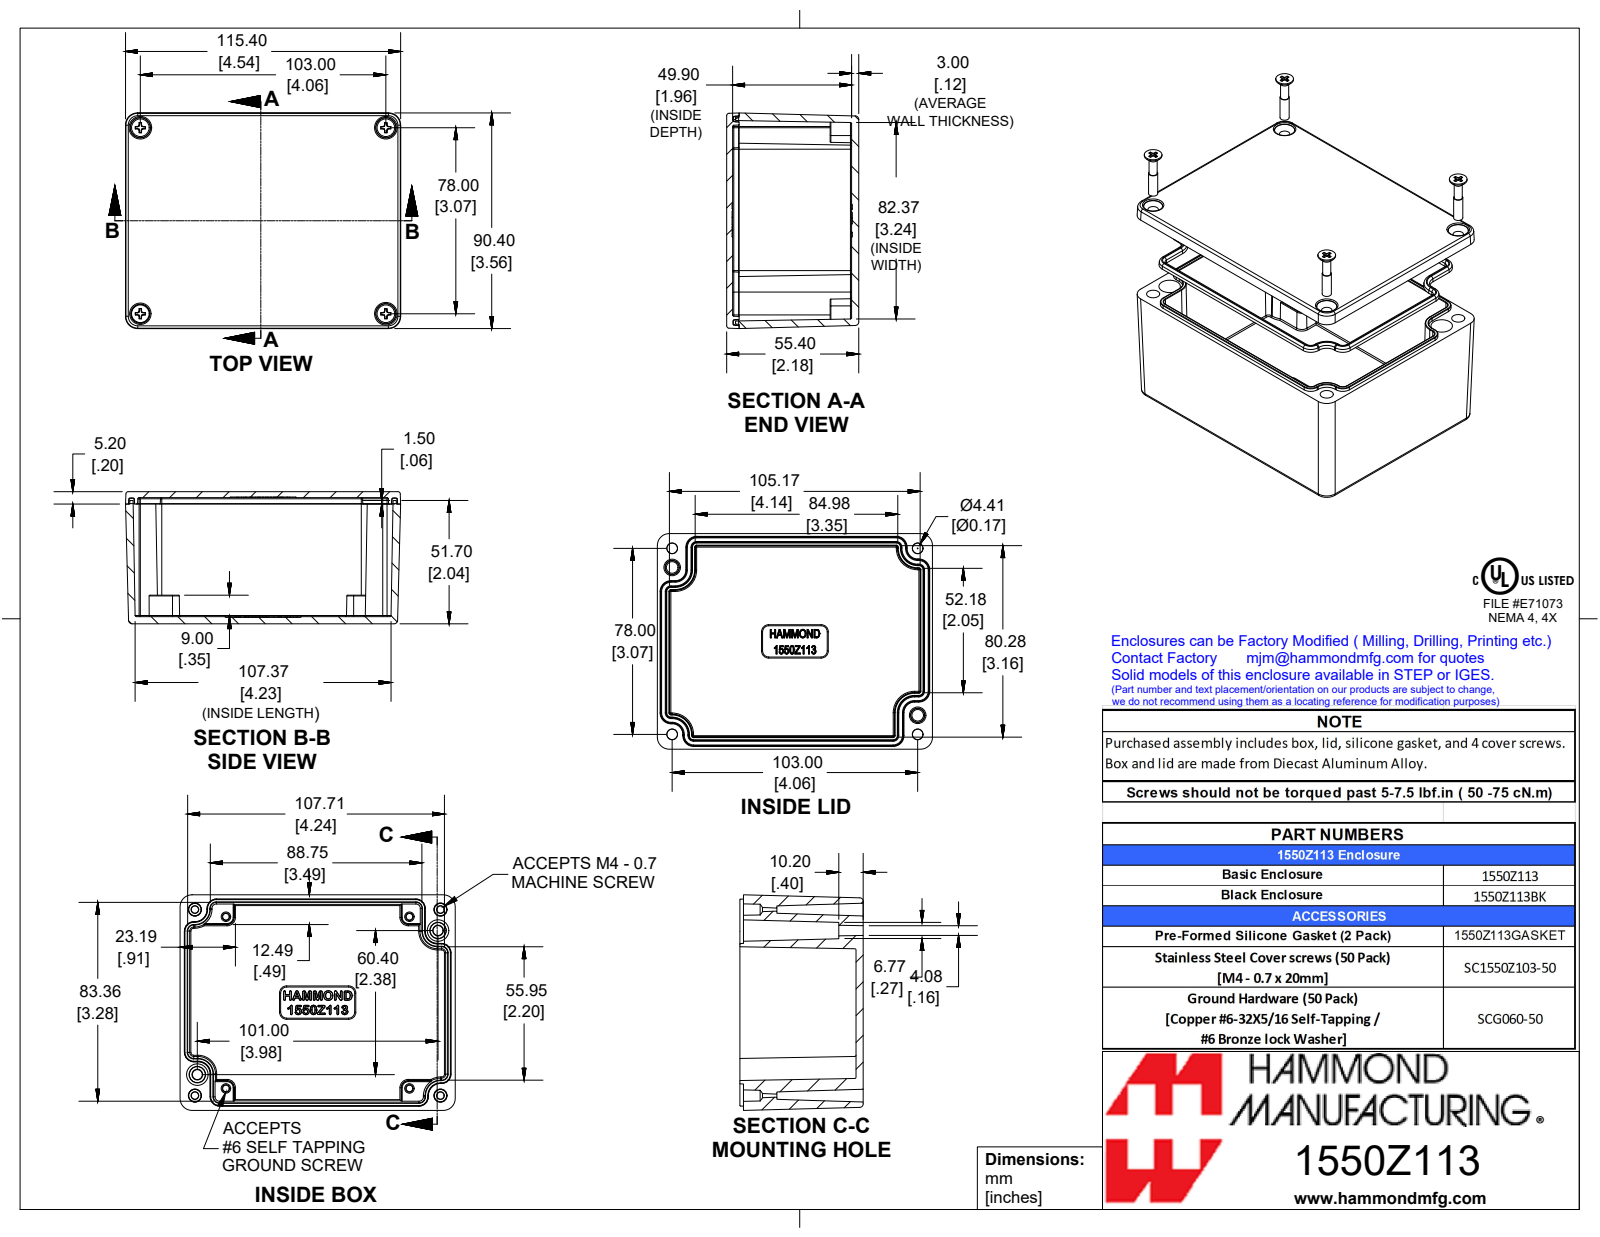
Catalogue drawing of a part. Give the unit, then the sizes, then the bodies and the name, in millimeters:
Units: millimetres
Overall size (bounding box): 115.4 × 90.4 × 55.8
Round bosses / shafts (diameter × count): ⌀7.5 ×4, ⌀3.9 ×4, ⌀3.3 ×4
Partial cylindrical surfaces — rounded edges, fillets, slot ends (radius × count): R0.2 ×60, R0.5 ×34, R0.3 ×28, R1 ×28, R5 ×8, R1.5 ×4
Main face-to-face distances: 55.4, 2.5, 3, 52.4, 52.9, 49.9, 2.7, 50.2, 47.2, 5.2
Volume: 137 900 mm³ · Surface area: 93 480 mm²
Bodies: 7 solids, 1340 faces (422 planar, 238 cylindrical, 680 other)
Part name (STEP PRODUCT): 1550Z113
STEP written by: SolidWorks 2019 (AUTOMOTIVE_DESIGN)
